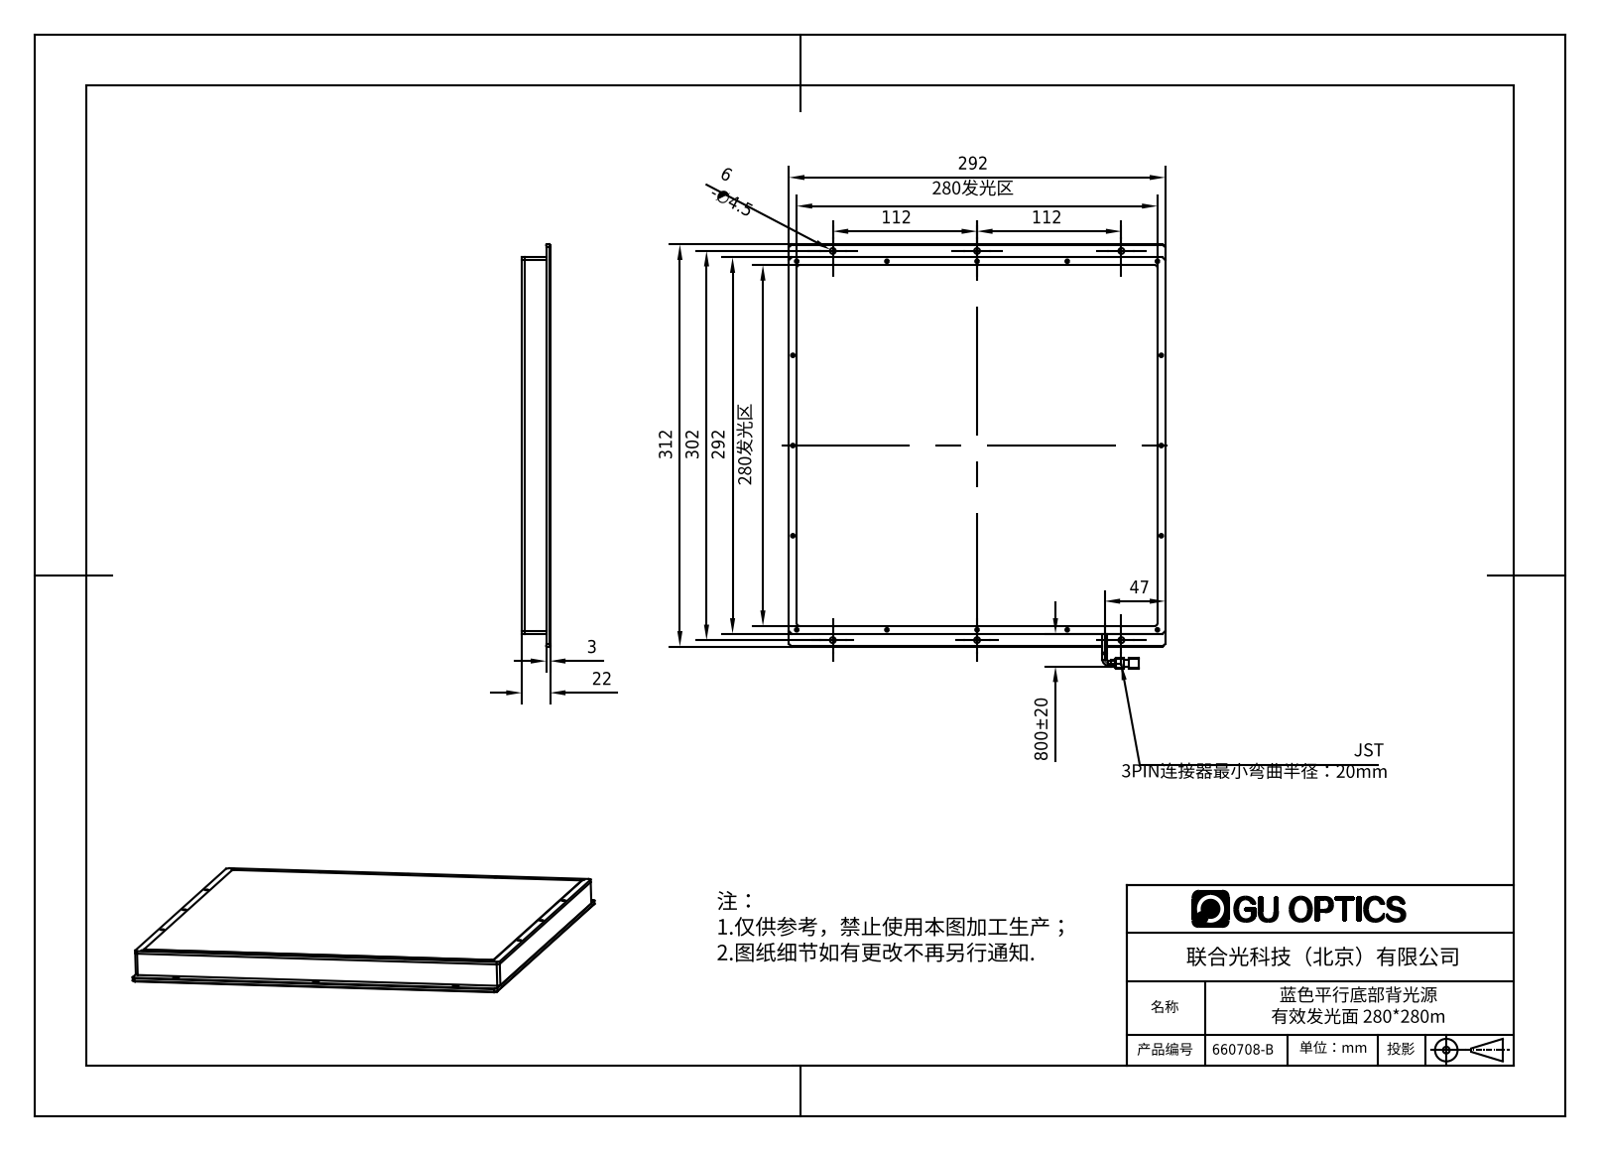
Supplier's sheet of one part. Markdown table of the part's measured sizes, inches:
| quantity | value |
| --- | --- |
| part name | 660708-B |
| STEP written by | SolidWorks 2016 (AUTOMOTIVE_DESIGN) |
| units | inches |
| bodies | 5 solids, 652 faces (220 planar, 274 cylindrical, 158 other) |
| overall size | 12.953 × 11.496 × 0.87 |
| volume | 34.46 in³ |
| surface area | 640.7 in² |
| round holes (diameter × count) | 0.063 × 32, 0.049 × 16, 0.059 × 16, 0.079 × 16, 0.094 × 16, 0.11 × 16, 0.177 × 6 |
| round bosses / shafts (diameter × count) | 0.138 × 2 |
| partial cylindrical surfaces (radius × count) | 0.02 × 8, 0.039 × 8, 0.079 × 6 |
| main face-to-face distances | 0.669, 0.118, 0.787, 0.752, 0.87, 0.083, 0.236, 11.26, 11.496, 11.024 |
| hole center spacings | 11.692, 3.15, 11.26, 4.155, 6.299, 7.261, 8.268, 10.394 |
